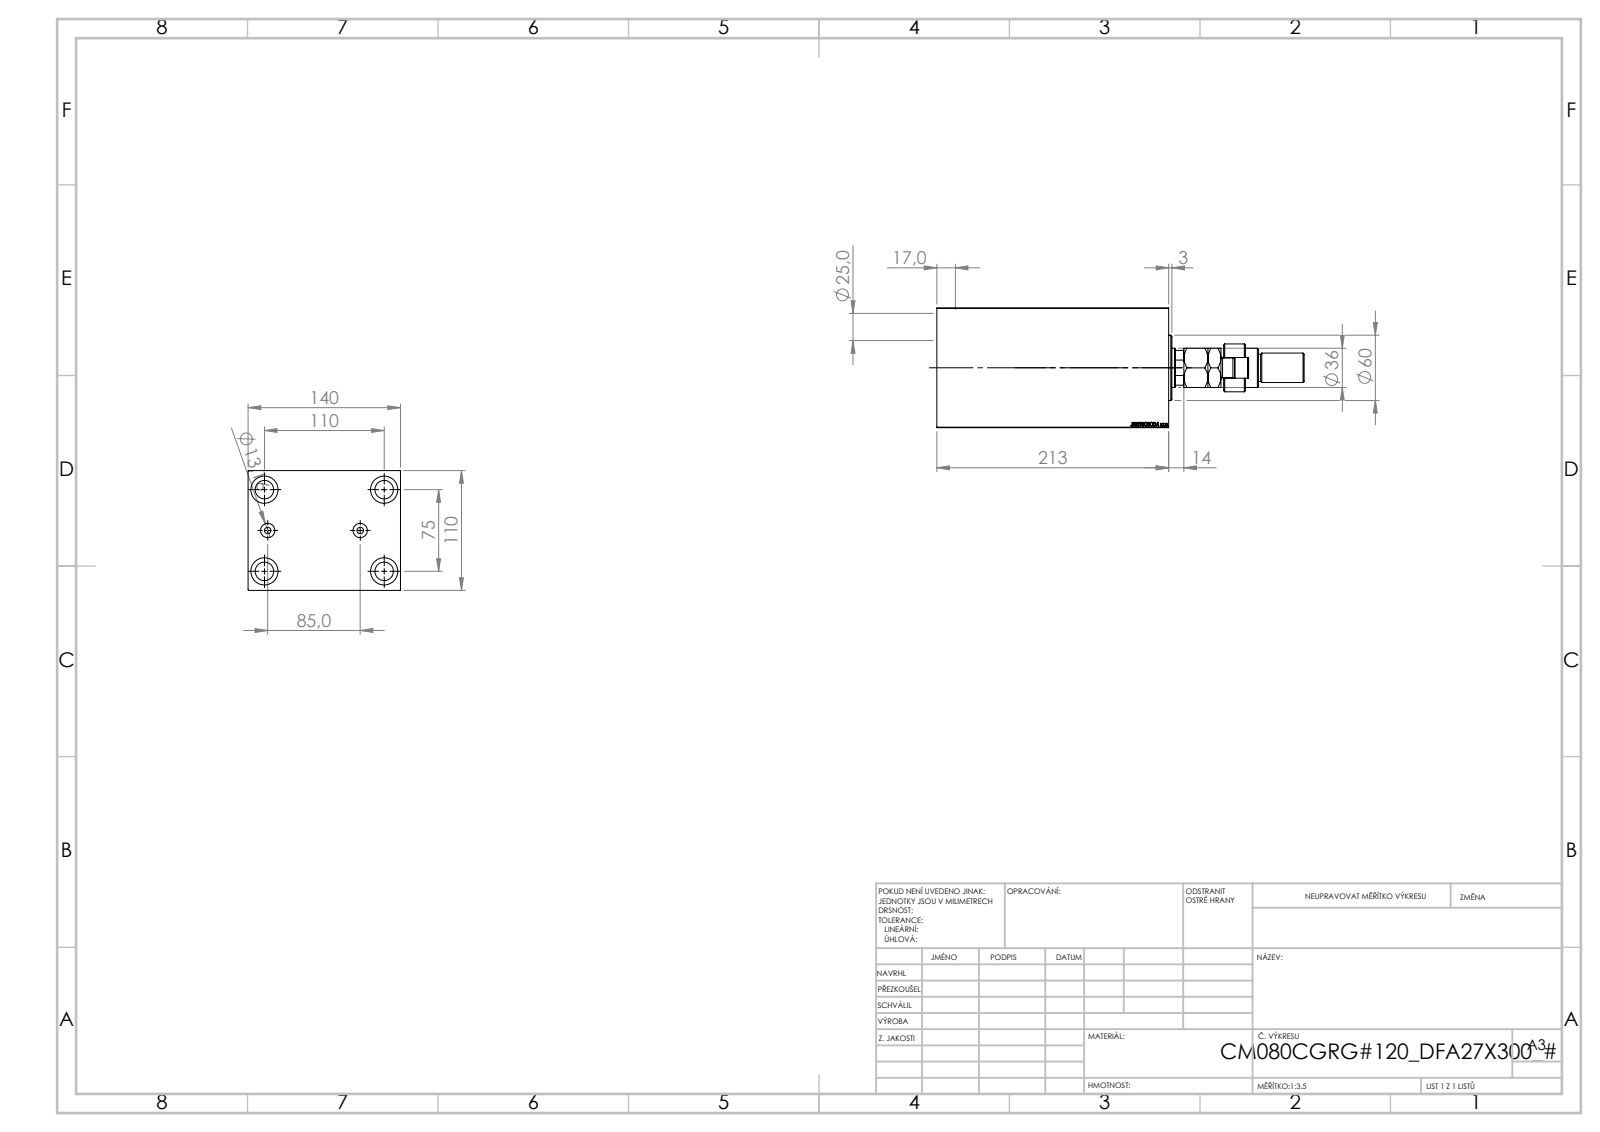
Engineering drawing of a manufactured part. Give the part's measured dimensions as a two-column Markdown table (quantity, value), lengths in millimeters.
| quantity | value |
| --- | --- |
| part name | V450CM_VC_B; FEMALE_PART_FOR_DFA; V450CM_C_VCP; MFA (+1 more) |
| STEP written by | SolidWorks 2019 (CONFIG_CONTROL_DESIGN) |
| units | millimeters |
| bodies | 5 solids, 948 faces (439 planar, 71 cylindrical, 438 other) |
| overall size | 337.5 × 140 × 110 |
| volume | 2 656 000 mm³ |
| surface area | 324 546 mm² |
| round holes (diameter × count) | 17 × 4, 25 × 4, 6 × 2, 13.16 × 2, 25.5 × 1, 39.5 × 1, 80 × 1, 82 × 1, 87 × 1 |
| round bosses / shafts (diameter × count) | 60 × 1, 44 × 1, 36 × 1, 28 × 1, 27 × 1, 25 × 1, 18 × 1 |
| partial cylindrical surfaces (radius × count) | 9.5 × 1, 15 × 1, 17.5 × 1 |
| main face-to-face distances | 110, 140, 213, 192, 21, 37.3, 154.7, 175.7, 157.3, 120 |
| hole center spacings | 39.53, 66.57, 104.46, 42.5, 75, 110, 133.14, 85 |
